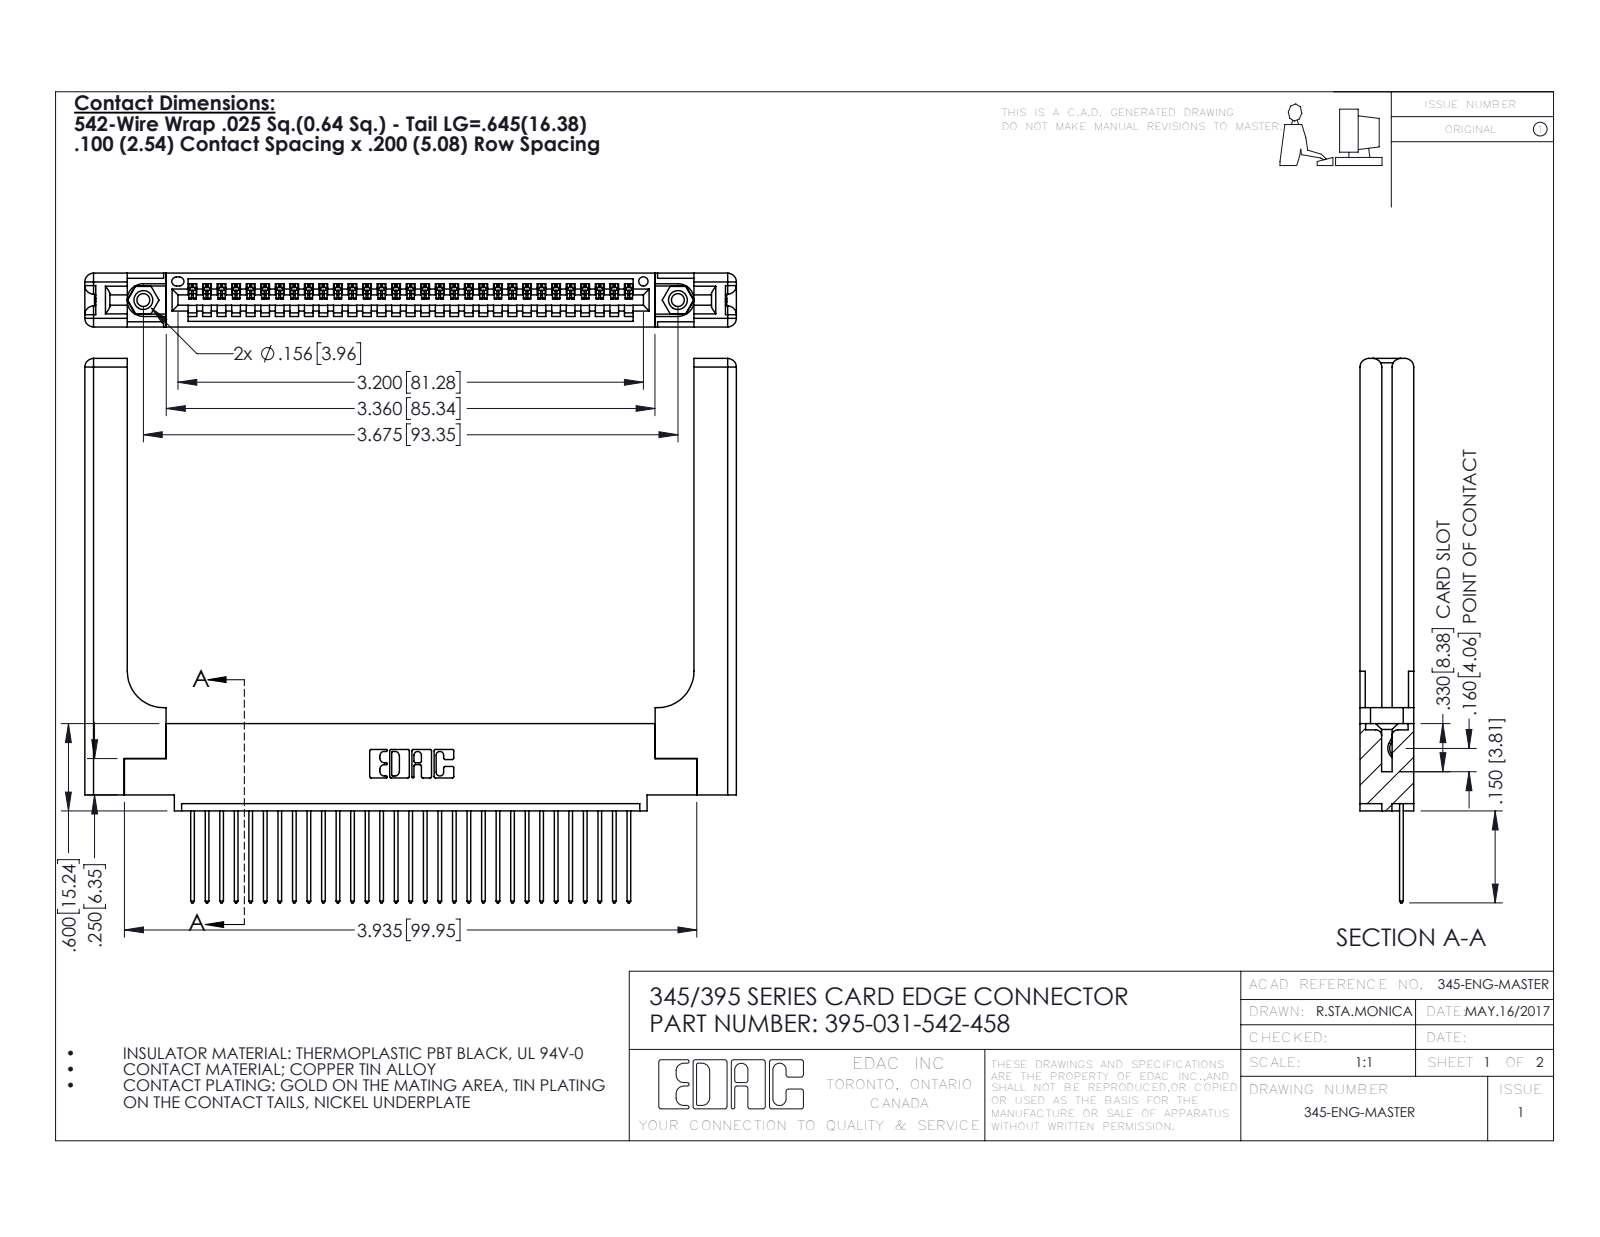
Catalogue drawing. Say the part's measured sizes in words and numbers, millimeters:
The part is named "345-292-001_345-293-142; 345-250-001_345-250-001-102; 345 Part_0.110 Offset - 0.156 Dia-TH; 395-031-542-458 (+1 more)". Its 3-D file was written by "SolidWorks 2016 (CONFIG_CONTROL_DESIGN)". It is 36 solids with 2184 faces: 1472 planar, 652 cylindrical and 60 other. Overall it measures 113.8 by 95 by 9.4 millimeters. Its volume is 19 220 cubic millimeters and its surface area 19 910 square millimeters. Round holes: 2 of diameter 2.3, 2 of diameter 3.2, 2 of diameter 4, 1 of diameter 1.6. Round bosses or shafts: 2 of diameter 3.9. Partial cylindrical surfaces (rounded edges, fillets, slot ends): 62 of radius 0.2, 62 of radius 0.3, 22 of radius 0.3, 16 of radius 1.5, 6 of radius 0.2, 6 of radius 0.8, 3 of radius 0.7, 2 of radius 0.8. The main face-to-face distances are 9.4, 1.8, 7.6, 2.5, 6.9, 0.6, 5.1, 3.8, 3.8, 2. The hole center spacings are 6.9, 87.4, 93.3.
